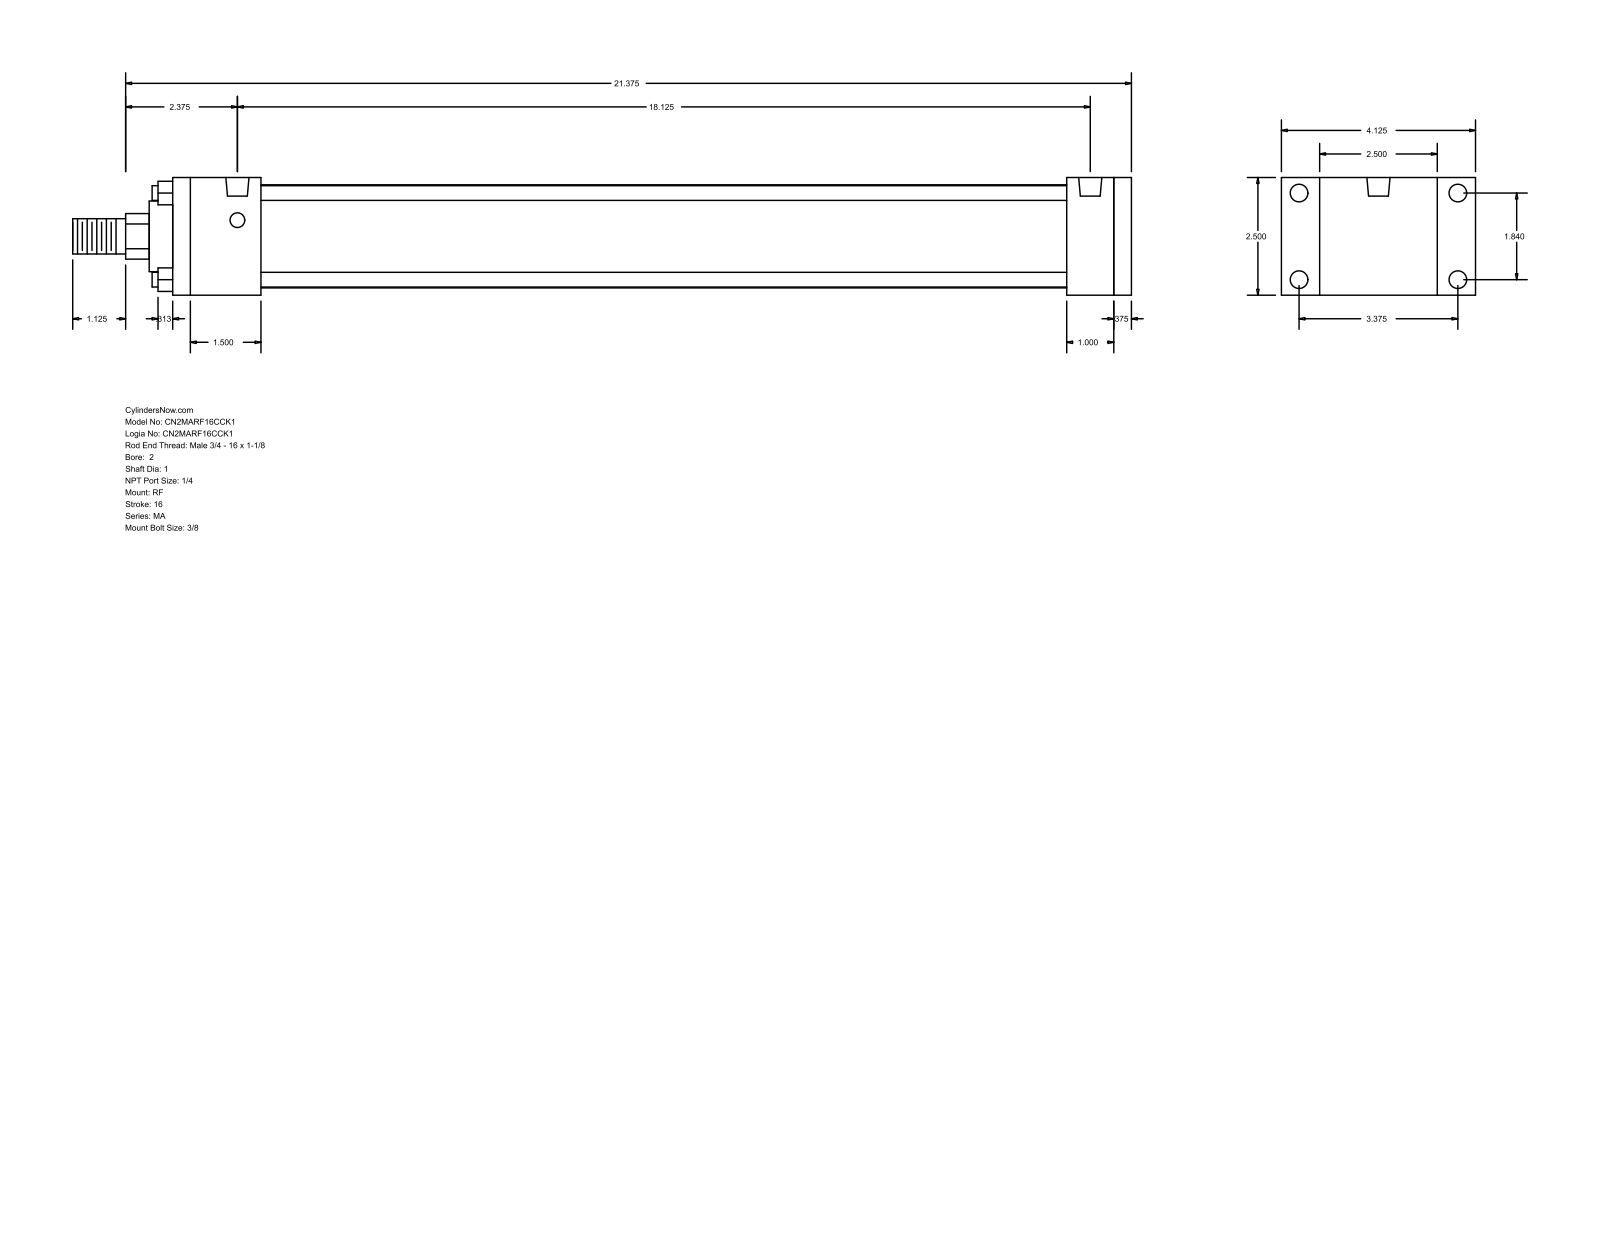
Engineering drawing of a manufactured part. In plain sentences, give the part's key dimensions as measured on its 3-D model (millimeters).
The part is named "MA_RF__0200_1". Its 3-D file was written by "GSSL Pune (CONFIG_CONTROL_DESIGN)". It is 0 solids with 92 faces: 64 planar, 28 cylindrical and 0 other. Overall it measures 571.5 by 104.78 by 63.5 millimeters. Round holes: 4 of diameter 7.94, 4 of diameter 9.53, 2 of diameter 12.49. Round bosses or shafts: 4 of diameter 7.94, 1 of diameter 55.63, 1 of diameter 38.1, 1 of diameter 25.4, 1 of diameter 19.05. Partial cylindrical surfaces (rounded edges, fillets, slot ends): 1 of radius 12.29. The main face-to-face distances are 63.5, 508, 9.52, 517.52, 25.4, 20.64, 12.7, 47.63, 460.37, 469.89. The hole center spacings are 46.74, 85.72, 97.63, 460.37.
